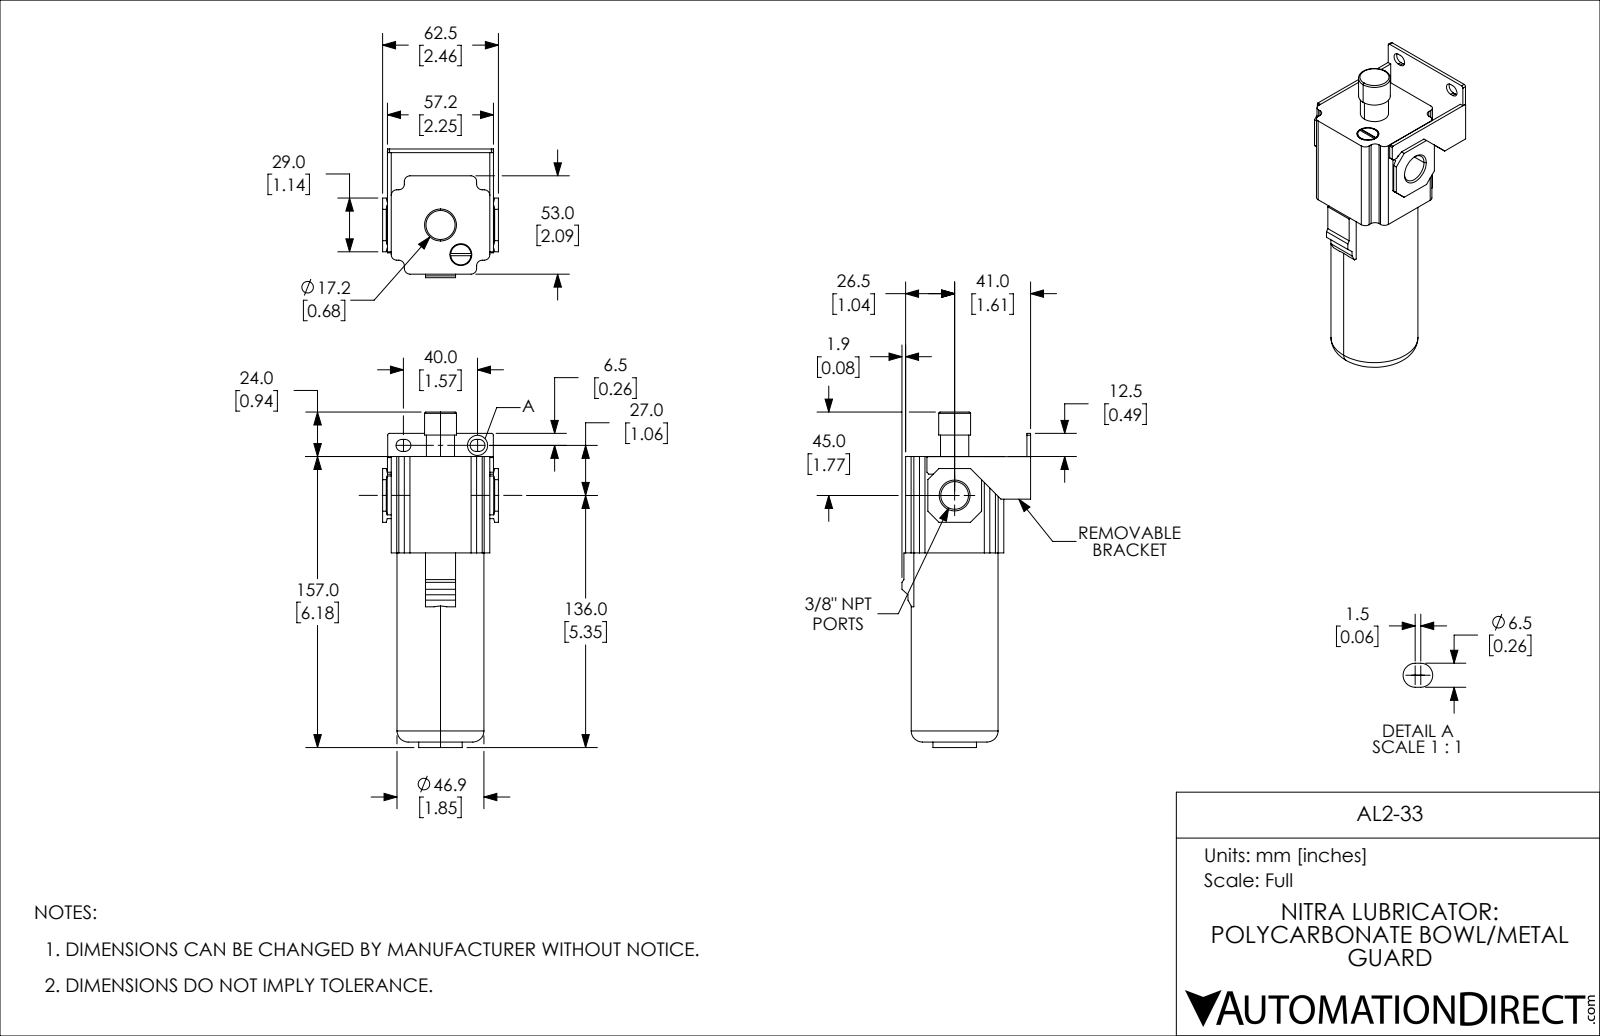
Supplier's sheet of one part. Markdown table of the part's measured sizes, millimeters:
| quantity | value |
| --- | --- |
| part name | AL2-33 |
| STEP written by | SolidWorks 2019 (CONFIG_CONTROL_DESIGN) |
| units | millimeters |
| bodies | 1 solid, 138 faces (96 planar, 34 cylindrical, 8 other) |
| overall size | 181 × 69.42 × 62.5 |
| volume | 325 884 mm³ |
| surface area | 41 369 mm² |
| round holes (diameter × count) | 11.8 × 1, 14.95 × 1 |
| round bosses / shafts (diameter × count) | 46.9 × 1, 23.5 × 1, 17.2 × 1, 15.2 × 1, 11 × 1 |
| partial cylindrical surfaces (radius × count) | 3 × 12, 3.25 × 4, 1 × 2 |
| main face-to-face distances | 2, 12.5, 14.5, 67.5, 65.5, 53, 55.2, 53.2, 2.65, 4.65 |
